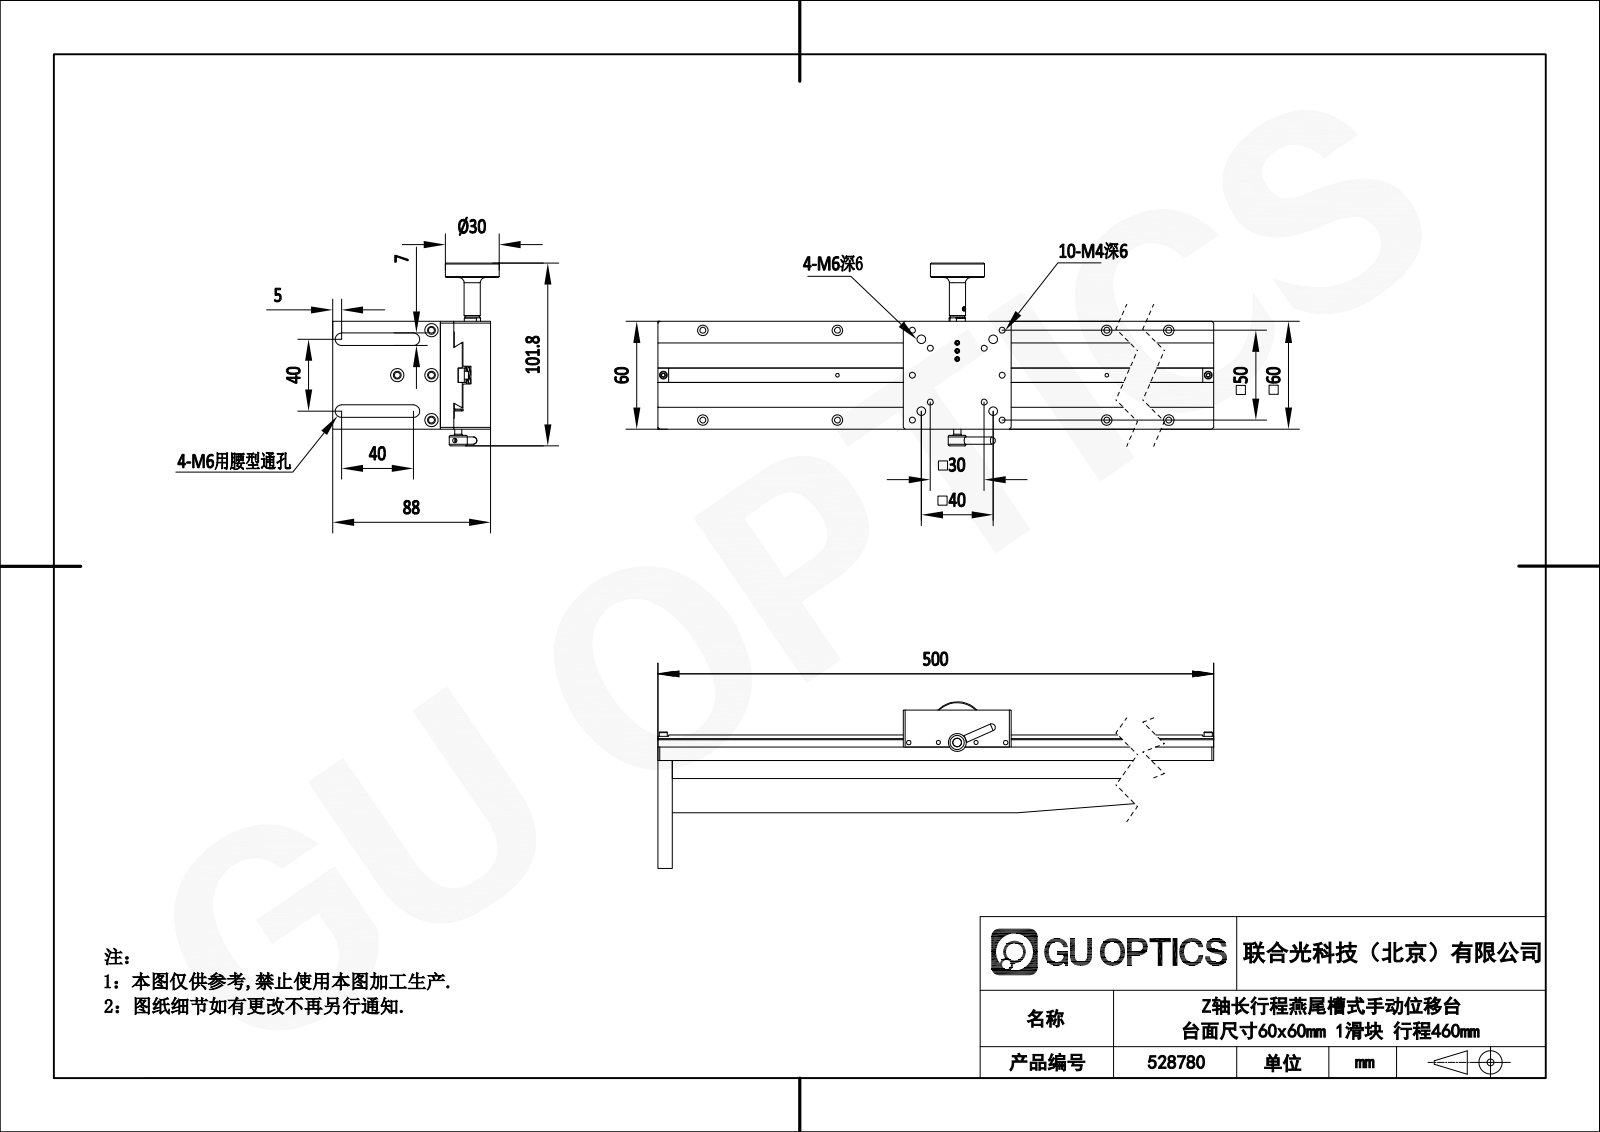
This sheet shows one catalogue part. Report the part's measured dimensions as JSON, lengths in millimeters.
{"part_name": "BWZ60-500-QCJ", "step_written_by": "SolidWorks 2024 (CONFIG_CONTROL_DESIGN)", "units": "millimeters", "bodies": {"solids": 27, "faces": 848, "planar": 317, "cylindrical": 321, "other": 210}, "overall_size": [500, 101.79, 92.73], "volume_mm3": 702351, "surface_area_mm2": 198013, "round_holes": [[3.3, 29], [4.5, 21], [6, 14], [2.5, 10], [5, 10], [2.05, 7], [2.9, 7], [7.5, 4], [4, 1], [4.1, 1], [8, 1], [10, 1]], "round_bosses_or_shafts": [[4.5, 7], [2.5, 7], [3, 5], [9, 2], [4, 2], [30, 1], [10, 1], [8, 1]], "partial_cylinders_radius": [[1.05, 6], [3.5, 4]], "face_to_face_distances": [10, 17.5, 7.5, 22.2, 12.2, 4.7, 24, 36, 60, 19.9], "hole_center_spacings": [75, 79.06, 25, 50, 90.14, 152.07, 150, 55.9]}
